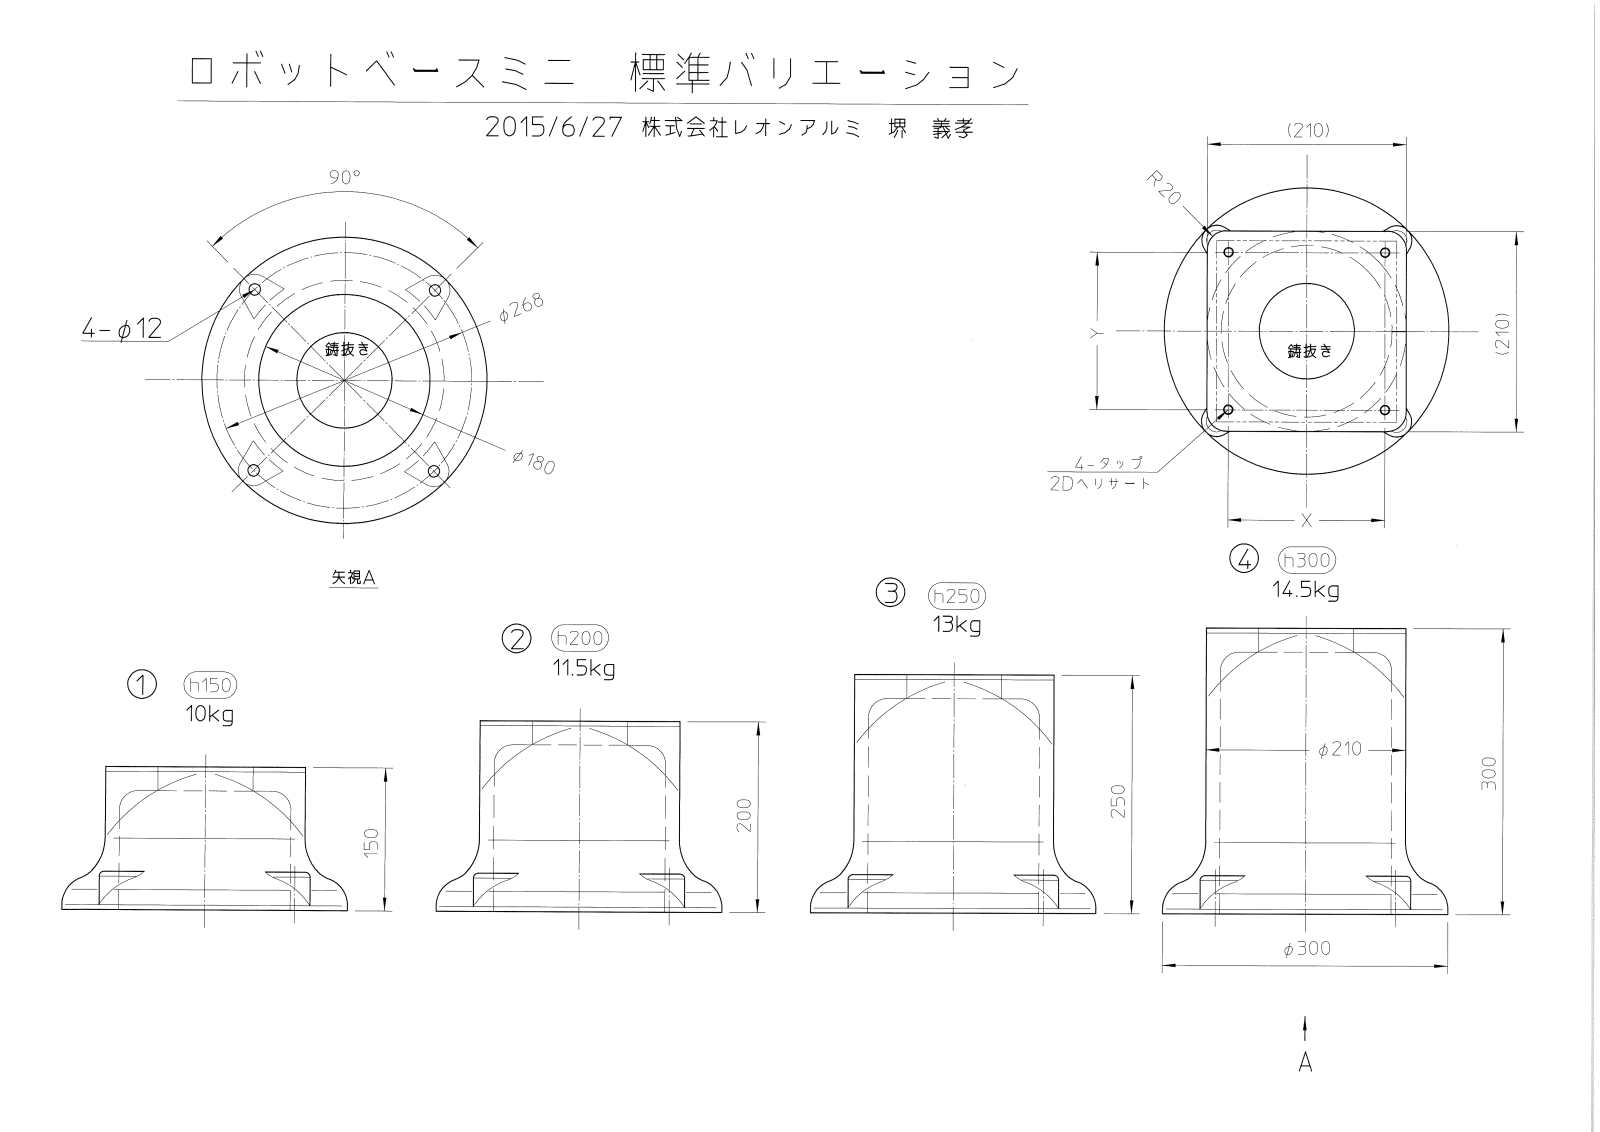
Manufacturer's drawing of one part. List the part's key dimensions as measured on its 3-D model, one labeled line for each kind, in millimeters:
Part name (STEP PRODUCT): パーツ66
STEP written by: Spatial InterOp 3D (CONFIG_CONTROL_DESIGN)
Units: millimetres
Bodies: 4 solids, 404 faces (76 planar, 176 cylindrical, 152 other)
Overall size (bounding box): 1500 × 300 × 300
Volume: 16 180 000 mm³ · Surface area: 1 608 000 mm²
Round holes (diameter × count): ⌀11 ×16, ⌀100 ×4, ⌀180 ×4
Round bosses / shafts (diameter × count): ⌀300 ×4, ⌀210 ×4
Partial cylindrical surfaces — rounded edges, fillets, slot ends (radius × count): R5 ×32, R10 ×32, R17.62 ×16, R50 ×16, R150 ×16
Main face-to-face distances: 50, 100, 150, 25, 75, 200, 300, 250, 125, 175
Hole centre spacings: 189.51, 400, 134, 442.62, 800, 268.01, 822.14, 210.49
